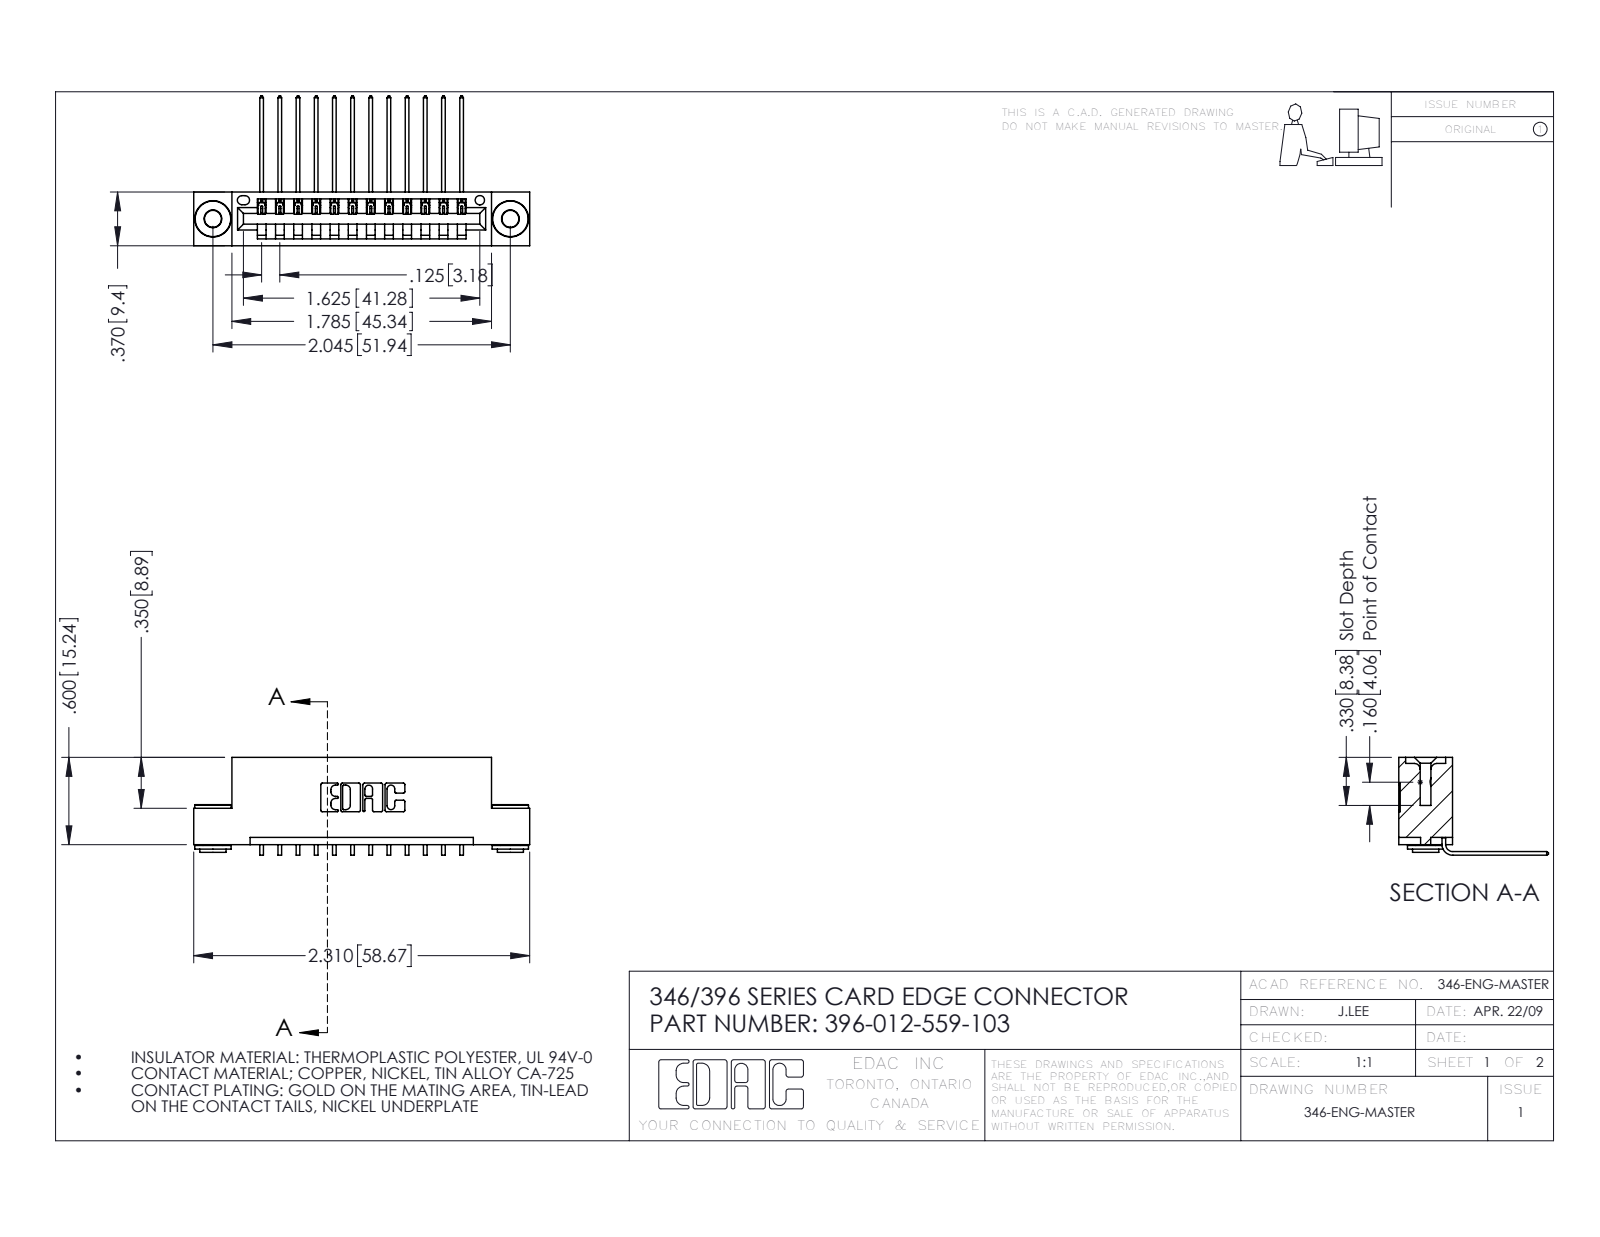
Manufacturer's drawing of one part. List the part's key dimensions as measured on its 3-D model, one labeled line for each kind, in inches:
Part name (STEP PRODUCT): 346 Part_Flush Mounting Lugs - 0.156 Dia-TH; 396-012-559-103; 345-250-002_345-250-002-102; 345-292-001_558 559 Tail - 1
STEP written by: SolidWorks 2016 (CONFIG_CONTROL_DESIGN)
Units: inches
Bodies: 15 solids, 880 faces (590 planar, 282 cylindrical, 8 other)
Overall size (bounding box): 2.31 × 1.03 × 0.673
Volume: 0.334 in³ · Surface area: 10.8 in²
Round holes (diameter × count): ⌀0.116 ×2, ⌀0.156 ×2, ⌀0.064 ×1
Round bosses / shafts (diameter × count): ⌀0.25 ×2, ⌀0.18 ×2, ⌀0.136 ×2
Partial cylindrical surfaces — rounded edges, fillets, slot ends (radius × count): R0.006 ×24, R0.01 ×22, R0.007 ×6, R0.031 ×6, R0.026 ×3, R0.031 ×2, R0.04 ×2, R0.014 ×1
Main face-to-face distances: 0.25, 0.048, 0.322, 0.37, 0.025, 0.072, 0.298, 0.148, 0.222, 0.1
Hole centre spacings: 0.246, 1.839, 2.045
